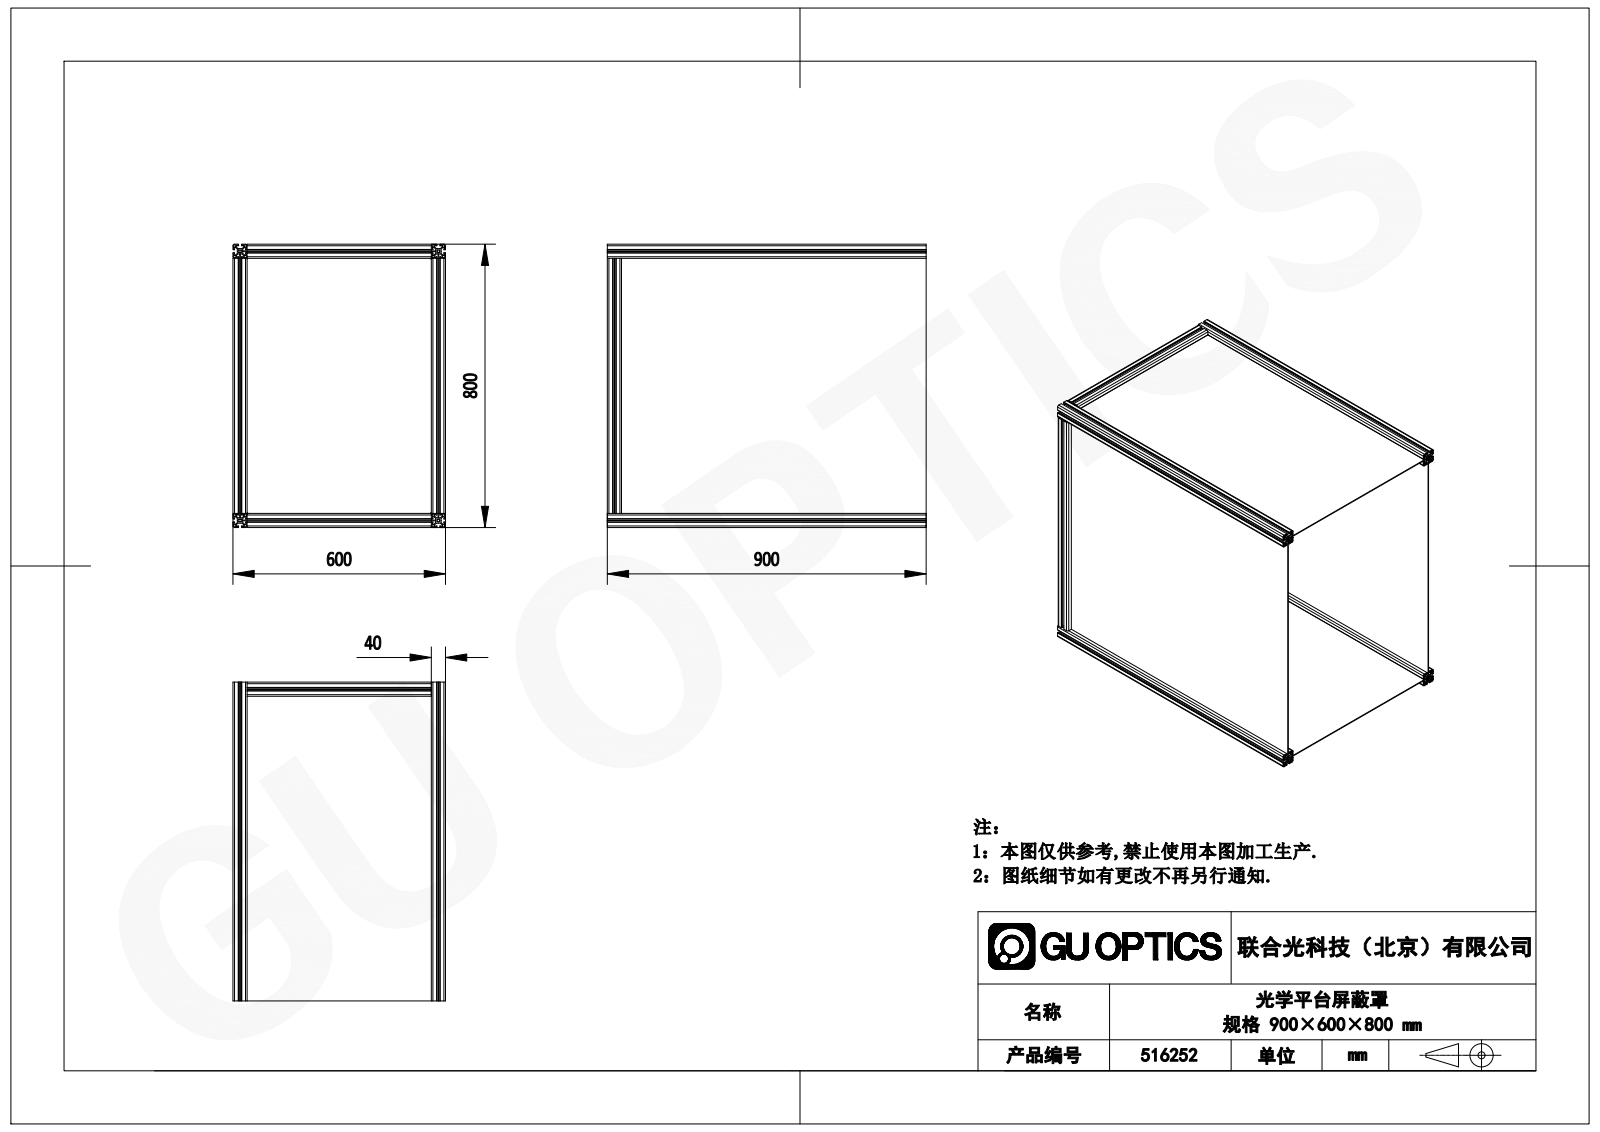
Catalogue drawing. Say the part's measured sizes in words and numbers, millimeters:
The part is named "光学平台屏蔽罩边框_720; 光学平台屏蔽罩面板_554_744; 光学平台屏蔽罩面板_554_872; 光学平台屏蔽罩面板_744_872 (+3 more)". Its 3-D file was written by "SolidWorks 2020 (CONFIG_CONTROL_DESIGN)". It is 13 solids with 1230 faces: 950 planar, 280 cylindrical and 0 other. Overall it measures 900 by 800 by 600 millimeters. Its volume is 8 944 000 cubic millimeters and its surface area 8 332 000 square millimeters. Partial cylindrical surfaces (rounded edges, fillets, slot ends): 64 of radius 0.5, 64 of radius 1, 32 of radius 0.75, 32 of radius 2.5, 32 of radius 4.5, 8 of radius 3.4. The main face-to-face distances are 2, 560, 760, 562, 558, 19, 21, 762, 758, 8.2.
